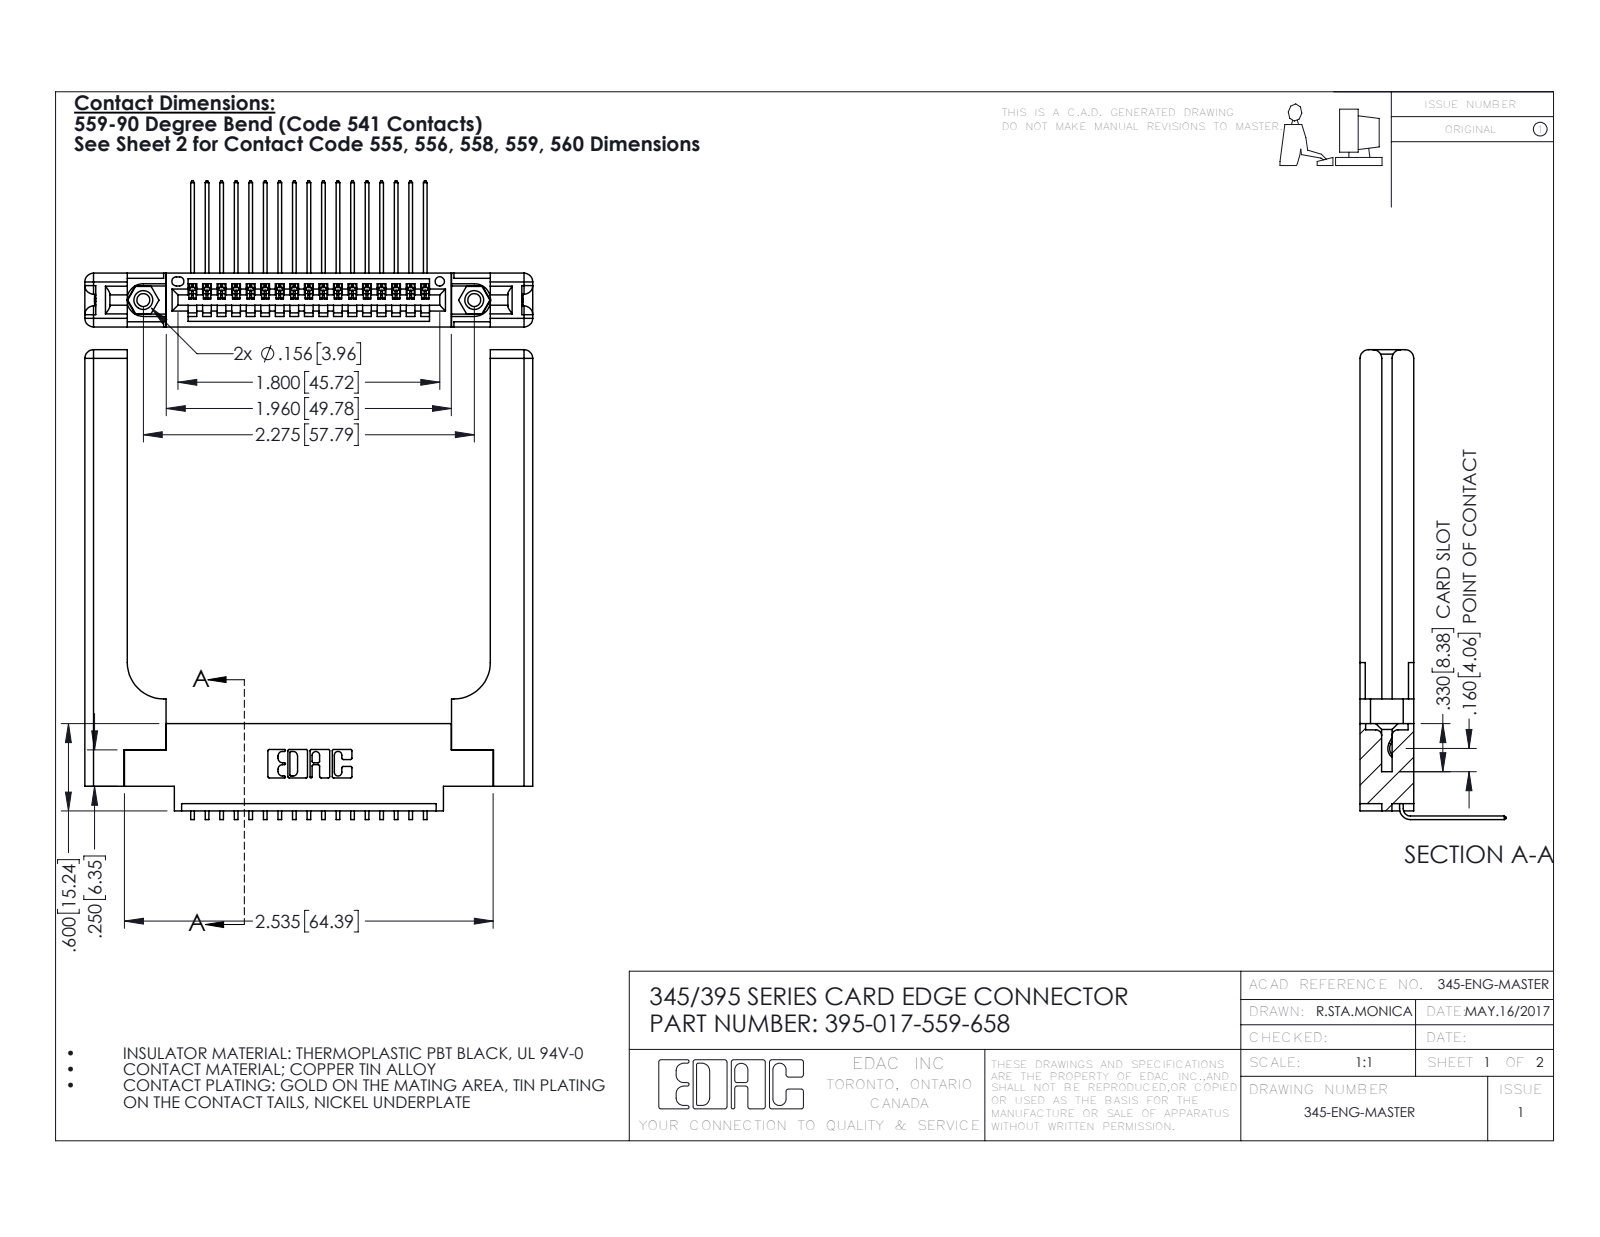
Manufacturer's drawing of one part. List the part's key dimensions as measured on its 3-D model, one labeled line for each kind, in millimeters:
Part name (STEP PRODUCT): 395-017-559-658; 345-250-001_345-250-001-102; 345-220-058_345-220-058; 345-292-001_558 559 Tail - 1 (+1 more)
STEP written by: SolidWorks 2016 (CONFIG_CONTROL_DESIGN)
Units: millimetres
Bodies: 22 solids, 1406 faces (946 planar, 400 cylindrical, 60 other)
Overall size (bounding box): 82 × 78.2 × 25.5
Volume: 15 700 mm³ · Surface area: 14 950 mm²
Round holes (diameter × count): ⌀2.3 ×2, ⌀3.2 ×2, ⌀4 ×2, ⌀1.6 ×1
Round bosses / shafts (diameter × count): ⌀3.9 ×2
Partial cylindrical surfaces — rounded edges, fillets, slot ends (radius × count): R0.2 ×34, R0.3 ×22, R1.5 ×16, R0.2 ×6, R0.8 ×6, R0.7 ×3, R0.8 ×2, R0.8 ×2
Main face-to-face distances: 9.4, 1.8, 7.6, 3.8, 3.8, 2, 5.6, 3.1, 3, 2.5
Hole centre spacings: 6.9, 51.8, 57.8
